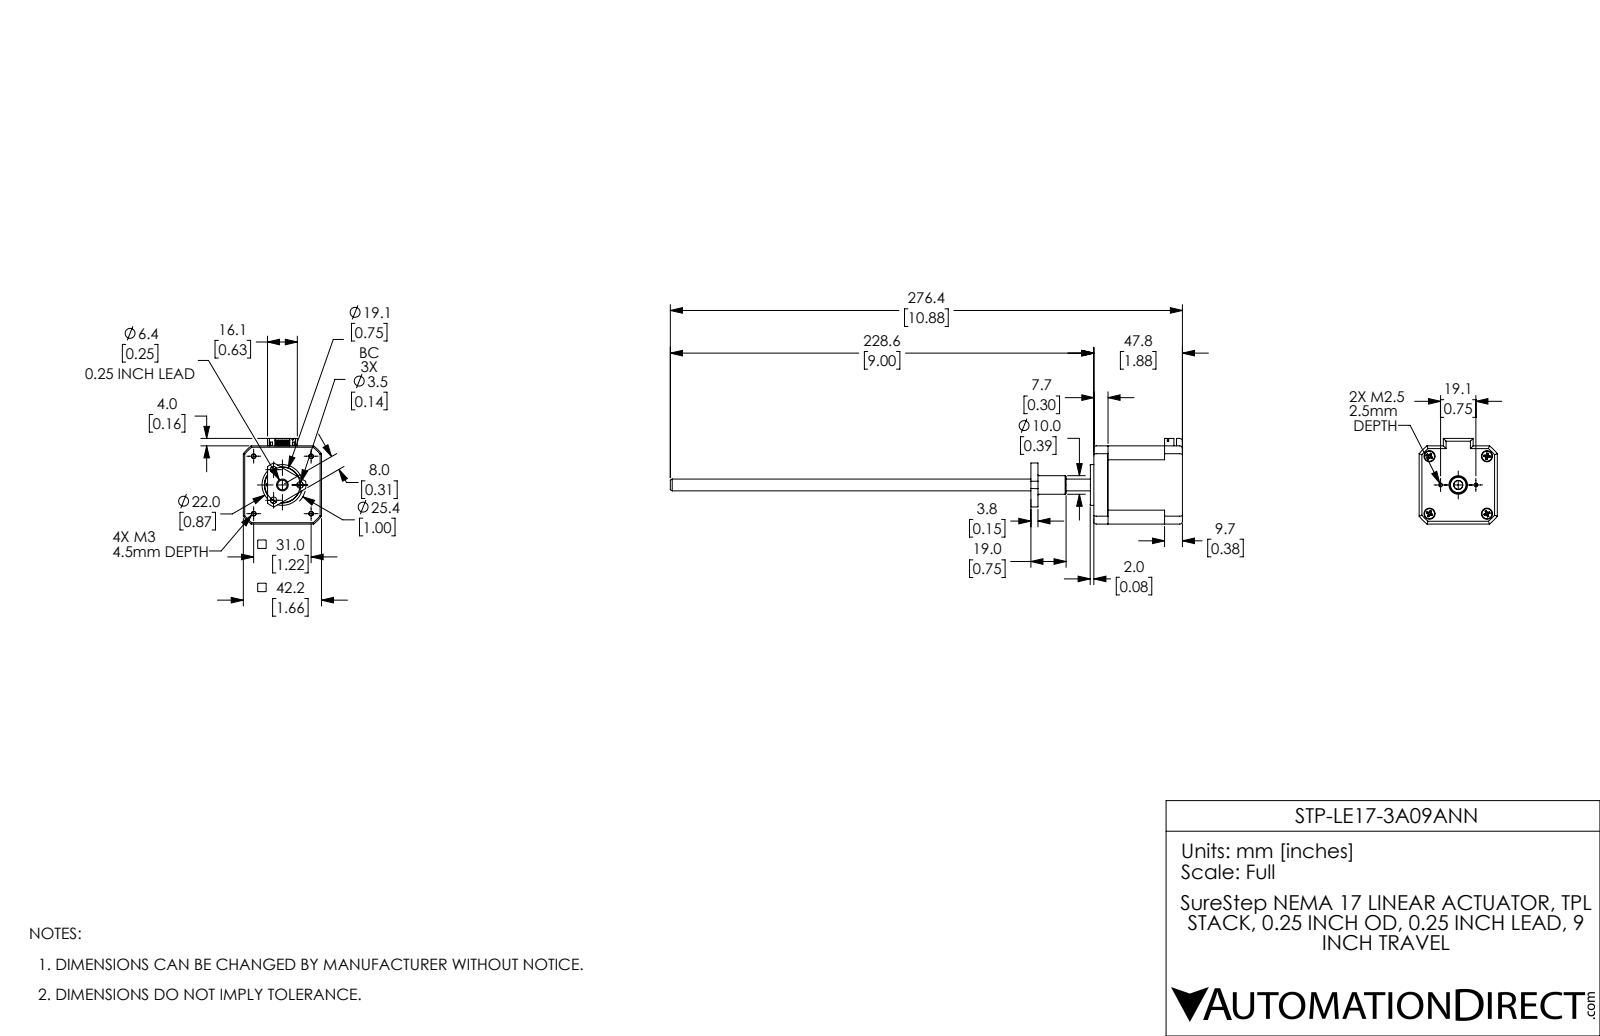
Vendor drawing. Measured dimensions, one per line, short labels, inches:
name: STP-LE17-3A09ANN_2; STP-LE17-3A09ANN; STP-LE17-3A09ANN_1
written by: SolidWorks 2017 (AUTOMOTIVE_DESIGN)
unit: in
bodies: 5 solids, 730 faces (364 planar, 236 cylindrical, 130 other)
size: 10.882 × 1.819 × 1.661
volume: 4.913 in³; area: 46.3 in²
holes: 4× ⌀0.098, 4× ⌀0.15, 4× ⌀0.236, 3× ⌀0.138, 2× ⌀0.059, 2× ⌀0.081, 1× ⌀0.193, 1× ⌀0.512, 1× ⌀0.669, 1× ⌀0.766, 1× ⌀0.787
bosses: 4× ⌀0.213, 4× ⌀0.115, 1× ⌀1.063, 1× ⌀1.02, 1× ⌀0.866, 1× ⌀0.472, 1× ⌀0.394, 1× ⌀0.354
rounds: 12× R0.039, 11× R0.059, 2× R0.098, 1× R0.028, 1× R0.5, 1× R0.561, 1× R0.63, 1× R0.988
face distances: 1.661, 0.38, 1.882, 1.581, 1.502, 0.063, 1.201, 0.301, 1.783, 1.598
hole spacings: 0.654, 0.375, 0.863, 1.159, 1.22, 0.194, 0.315, 0.51
